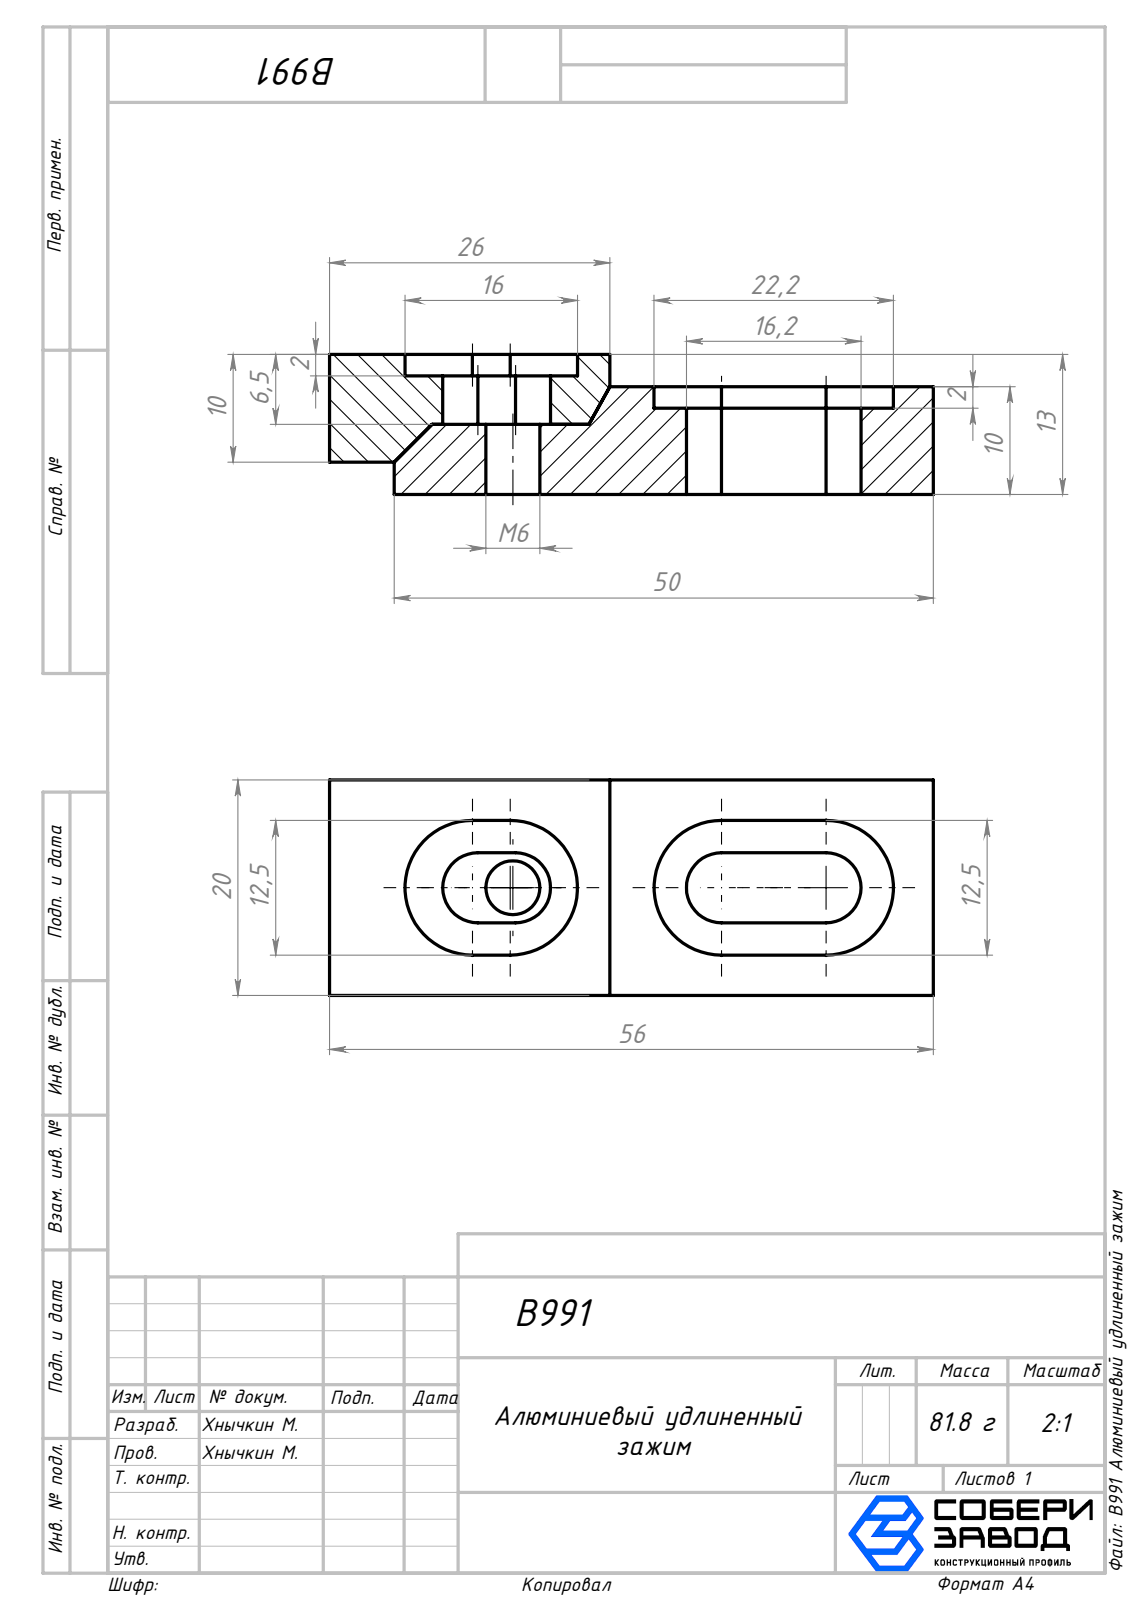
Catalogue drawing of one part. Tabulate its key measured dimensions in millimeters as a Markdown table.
| quantity | value |
| --- | --- |
| part name | B991 Алюминиевый удлиненный зажим_00; B991 Ал. зажим_2_00; B991 Алюминиевый удлиненный зажим |
| STEP written by | SolidWorks 2026 (AUTOMOTIVE_DESIGN) |
| units | millimeters |
| bodies | 2 solids, 41 faces (28 planar, 13 cylindrical, 0 other) |
| overall size | 56 × 20 × 13 |
| volume | 10 430 mm³ |
| surface area | 5 351 mm² |
| round holes (diameter × count) | 5 × 1 |
| partial cylindrical surfaces (radius × count) | 3.25 × 4, 6.25 × 4 |
| main face-to-face distances | 6.5, 20, 3, 10, 3.5, 13, 5, 8, 2, 56 |
